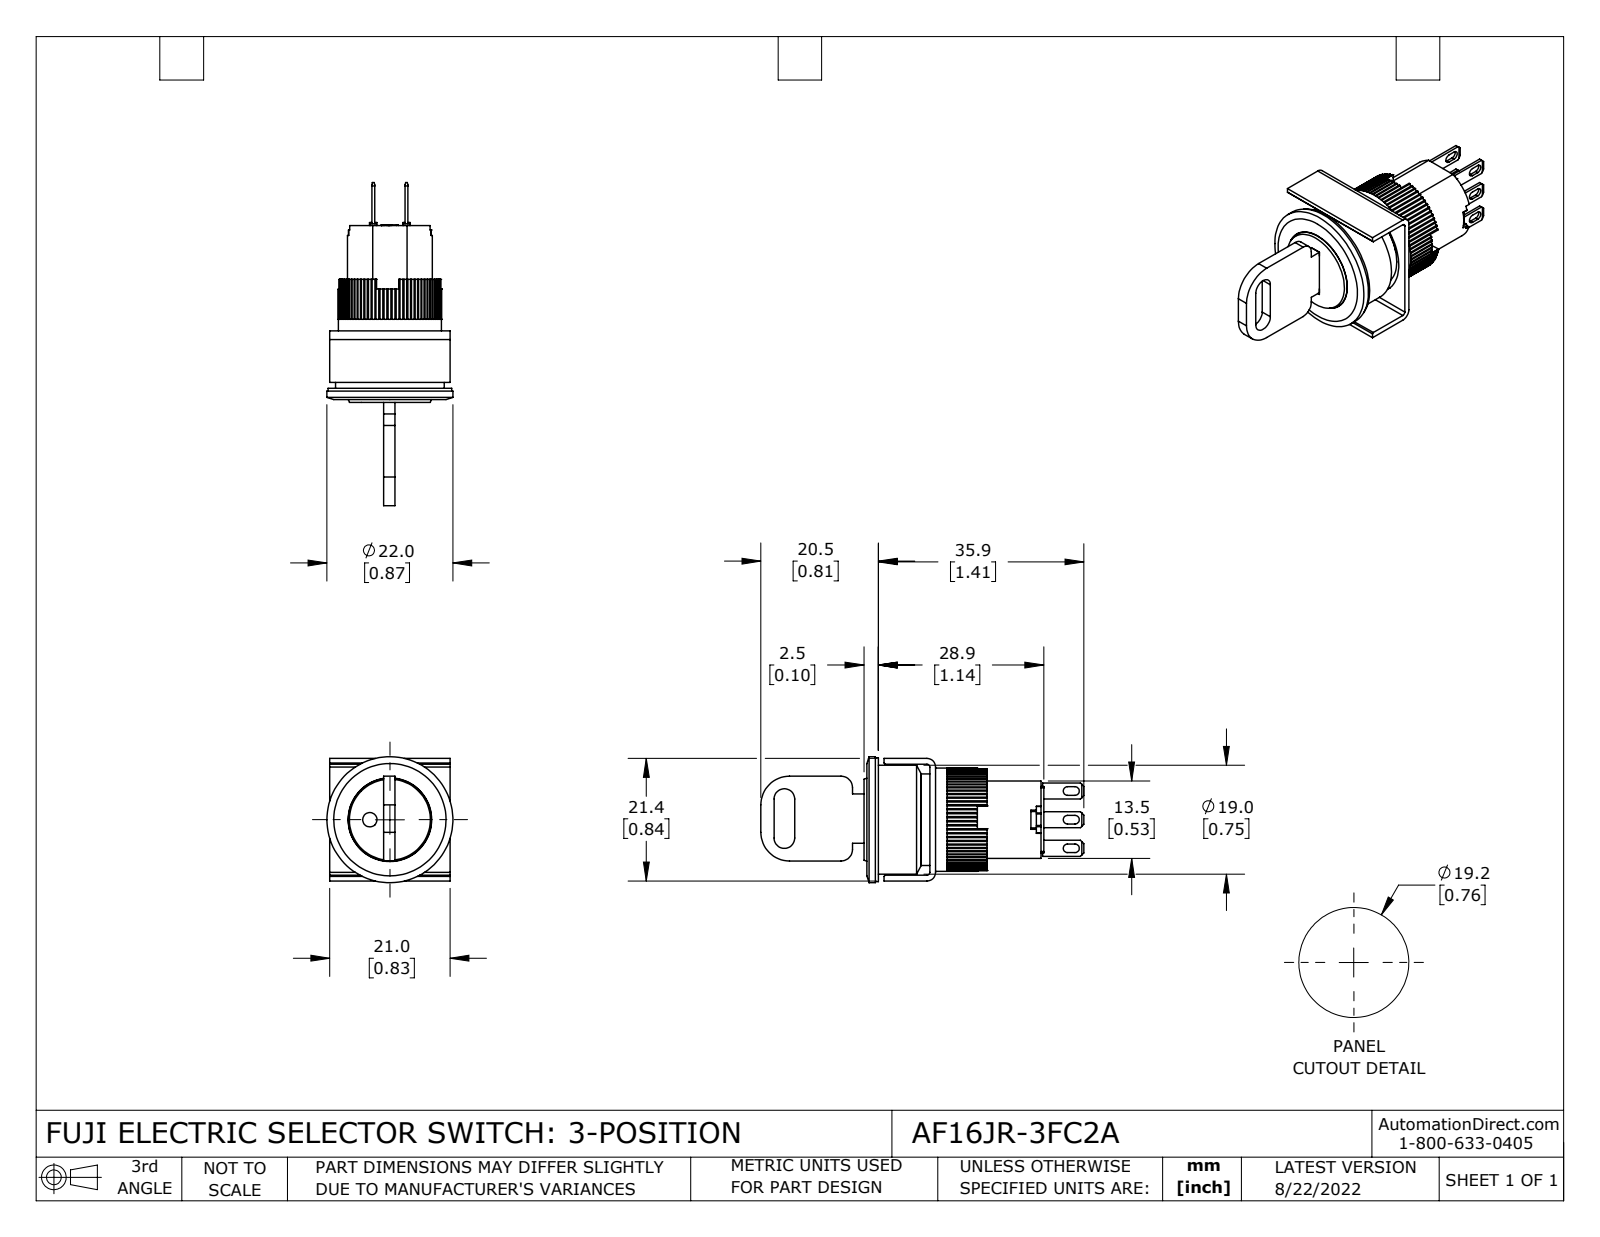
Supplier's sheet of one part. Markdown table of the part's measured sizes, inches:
| quantity | value |
| --- | --- |
| part name | AF16JR-3FC2A |
| STEP written by | SolidWorks 2021 (CONFIG_CONTROL_DESIGN) |
| units | inches |
| bodies | 13 solids, 707 faces (518 planar, 183 cylindrical, 6 other) |
| overall size | 2.22 × 0.866 × 0.866 |
| volume | 0.495 in³ |
| surface area | 11.24 in² |
| round holes (diameter × count) | 0.039 × 1, 0.098 × 1, 0.575 × 1, 0.709 × 1, 0.748 × 1 |
| round bosses / shafts (diameter × count) | 0.866 × 1, 0.85 × 1, 0.63 × 1, 0.583 × 1, 0.571 × 1 |
| partial cylindrical surfaces (radius × count) | 0.01 × 80, 0.008 × 12, 0.03 × 6, 0.02 × 2, 0.059 × 2, 0.071 × 2, 0.079 × 2, 0.197 × 2 |
| main face-to-face distances | 0.079, 0.039, 0.02, 0.374, 0.177, 0.098, 0.394, 0.803, 0.059, 0.764 |
| hole center spacings | 0.138 |
